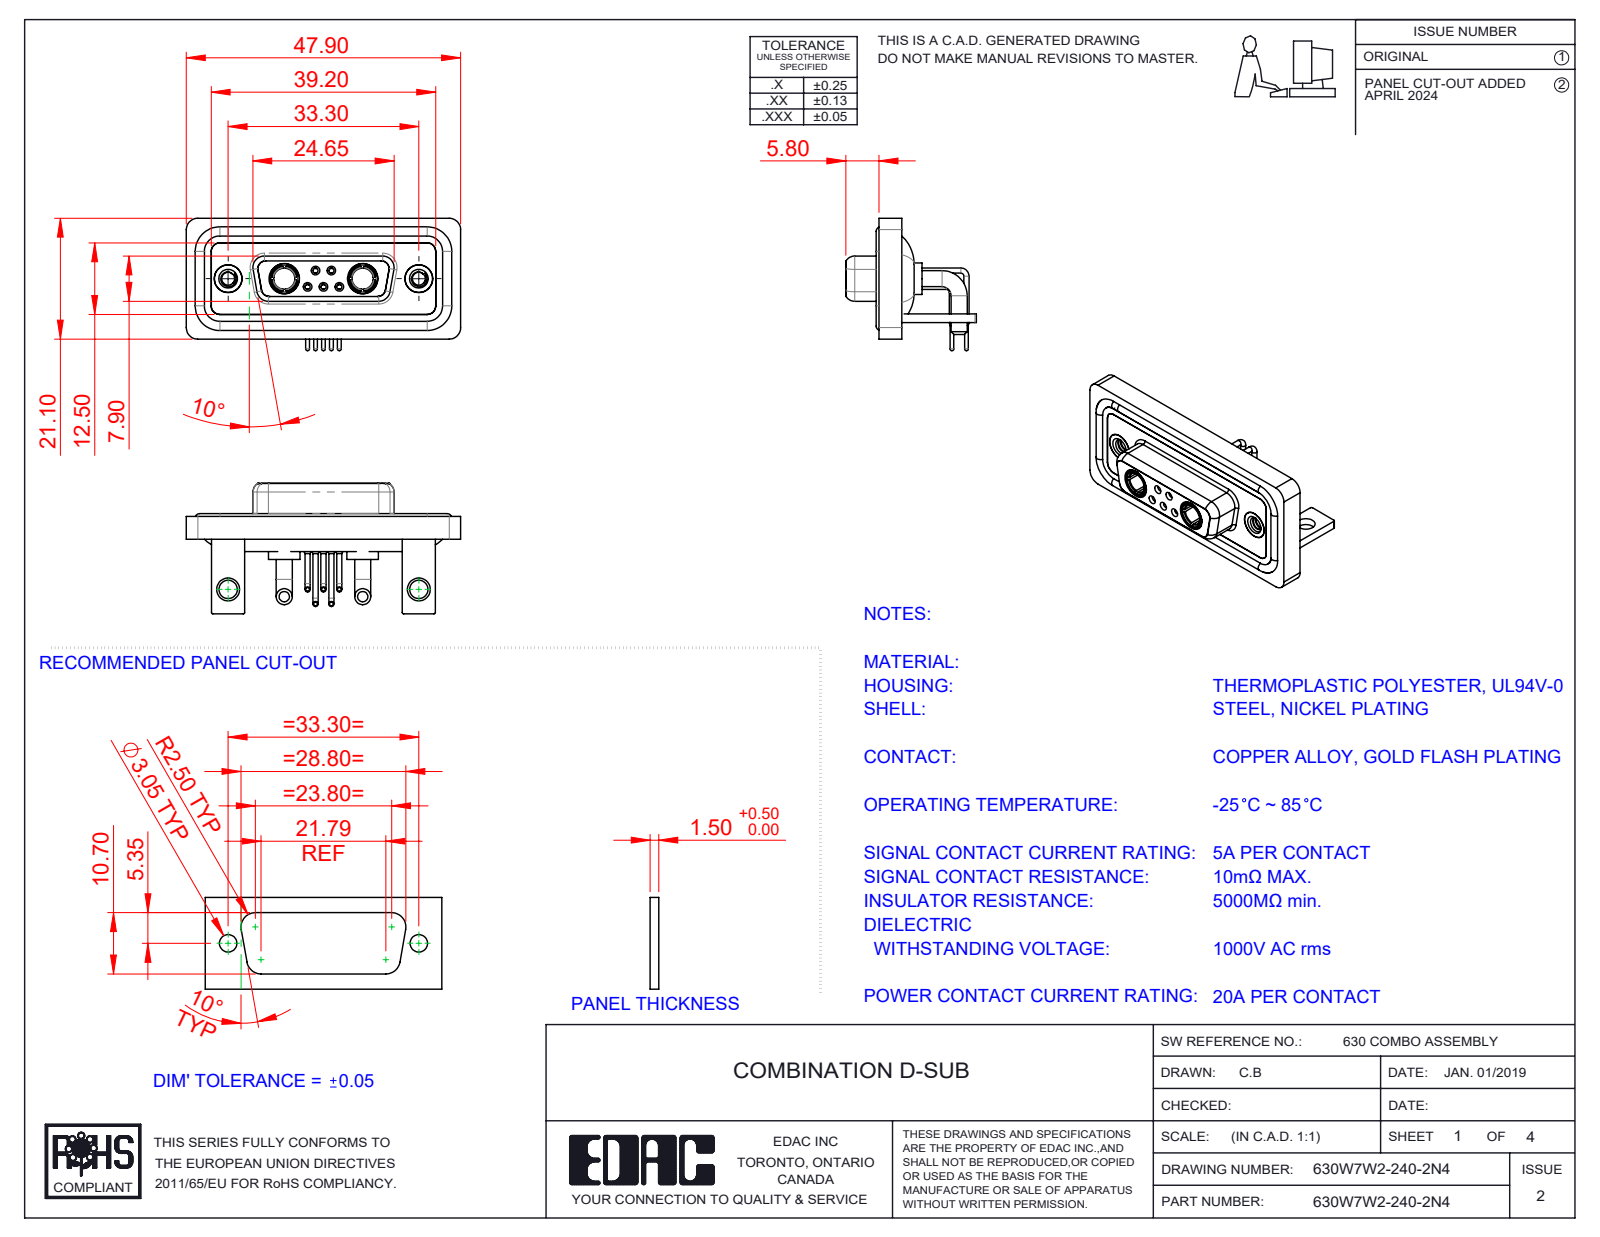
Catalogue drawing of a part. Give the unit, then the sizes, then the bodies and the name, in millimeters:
Units: millimetres
Overall size (bounding box): 47.9 × 23.12 × 22.8
Round holes (diameter × count): ⌀0.9 ×5, ⌀1.1 ×5, ⌀1.5 ×5, ⌀2 ×5, ⌀4.85 ×4, ⌀1.6 ×3, ⌀1.7 ×2, ⌀2.26 ×2, ⌀3.2 ×2, ⌀3.7 ×2, ⌀4 ×2, ⌀4.05 ×2
Round bosses / shafts (diameter × count): ⌀1.6 ×6, ⌀0.9 ×5, ⌀0.65 ×5, ⌀2.8 ×4, ⌀5.5 ×2, ⌀5.2 ×2, ⌀4.96 ×2, ⌀4.95 ×2
Partial cylindrical surfaces — rounded edges, fillets, slot ends (radius × count): R2 ×21, R1.5 ×18, R0.25 ×16, R1.35 ×12, R1.6 ×8, R0.5 ×5, R0.6 ×4, R0.65 ×4
Main face-to-face distances: 0.4, 2.9, 1.5, 1.8, 3.7, 1.1, 4.1, 1.6, 2.5, 1.4
Hole centre spacings: 3.16, 2.77, 9.8, 23.5, 33.3, 4.31, 4.33, 5.03
Volume: 6 563 mm³ · Surface area: 10 941 mm²
Bodies: 18 solids, 855 faces (258 planar, 377 cylindrical, 220 other)
Part name (STEP PRODUCT): 630Combo Threaded Rivet_2; 630Combo Housing_7W2; 630W7W2-240-2N4; 630Combo Waterproof Housing_15 Contacts (+6 more)
STEP written by: SolidWorks 2023 (CONFIG_CONTROL_DESIGN)
